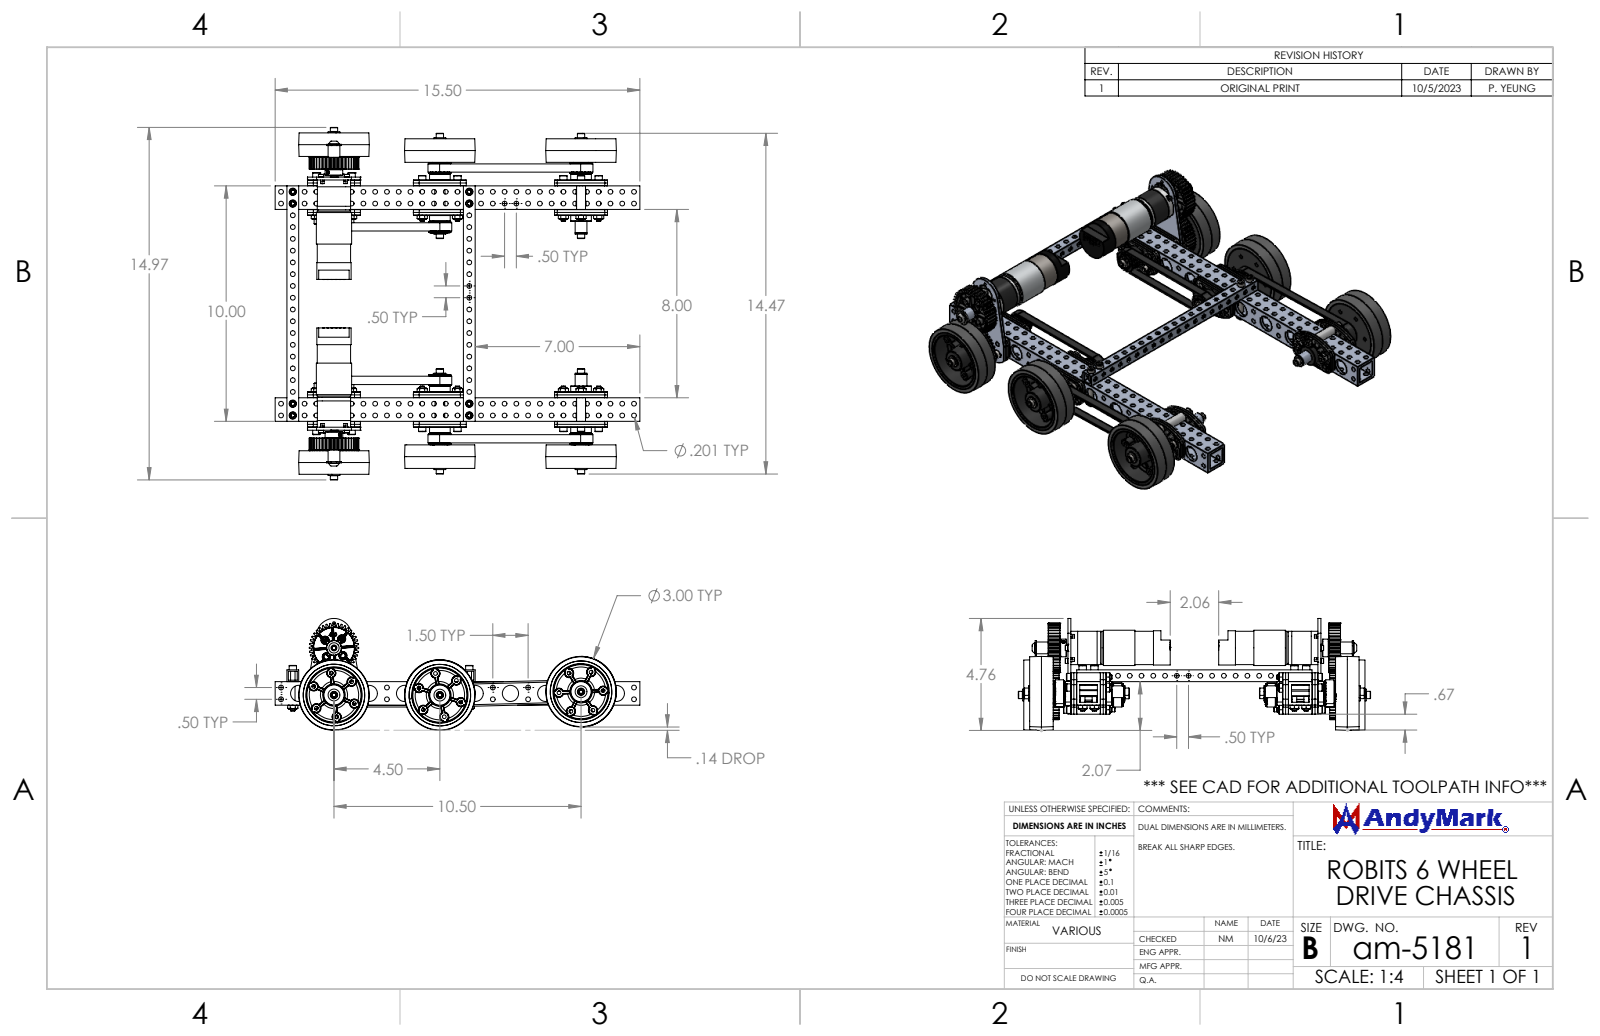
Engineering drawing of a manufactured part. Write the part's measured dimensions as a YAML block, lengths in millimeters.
part_name: "am-3104 NeveRest Motor; am-5003-0400 RoBits 0.375 in. Hex Shaft 4 in. Long; am-1063 10-32 Nylock Jam Nut_am-1063 10-32 Nylock Jam Nut; am-1002 10-32 x 0500 SHCS_am-1002 10-32 x 0500 SHCS (+8 more)"
step_written_by: "SolidWorks 2022 (AUTOMOTIVE_DESIGN)"
units: millimeters
bodies: {solids: 252, faces: 35722, planar: 7070, cylindrical: 10784, other: 17868}
overall_size: [393.7, 380.3, 120.7]
volume: 1143000
surface_area: 743900
round_holes:
  - {diameter: 5.1, count: 215}
  - {diameter: 4.2, count: 104}
  - {diameter: 4, count: 43}
  - {diameter: 4.1, count: 19}
  - {diameter: 6.1, count: 19}
  - {diameter: 2.5, count: 18}
  - {diameter: 17.4, count: 15}
  - {diameter: 3.2, count: 14}
  - {diameter: 3.2, count: 12}
  - {diameter: 4.8, count: 8}
  - {diameter: 4.9, count: 7}
  - {diameter: 10.9, count: 6}
round_bosses_or_shafts:
  - {diameter: 4.8, count: 18}
  - {diameter: 8, count: 13}
  - {diameter: 7.9, count: 13}
  - {diameter: 5.5, count: 12}
  - {diameter: 3, count: 12}
  - {diameter: 15.9, count: 7}
  - {diameter: 12.7, count: 7}
  - {diameter: 9.5, count: 7}
partial_cylinders:
  - {radius: 0.3, count: 1776}
  - {radius: 0.4, count: 294}
  - {radius: 10.2, count: 246}
  - {radius: 1.7, count: 191}
  - {radius: 1.6, count: 68}
  - {radius: 0.8, count: 32}
  - {radius: 5.1, count: 28}
  - {radius: 5.6, count: 28}
face_to_face_distances: [25.4, 19.1, 31.8, 228.6, 254, 260.4, 6.4, 50.8, 279.4, 22.2]
hole_center_spacings: [12.7, 38.1, 76.2, 114.3, 25.4, 40.2, 20.1, 50.8]
